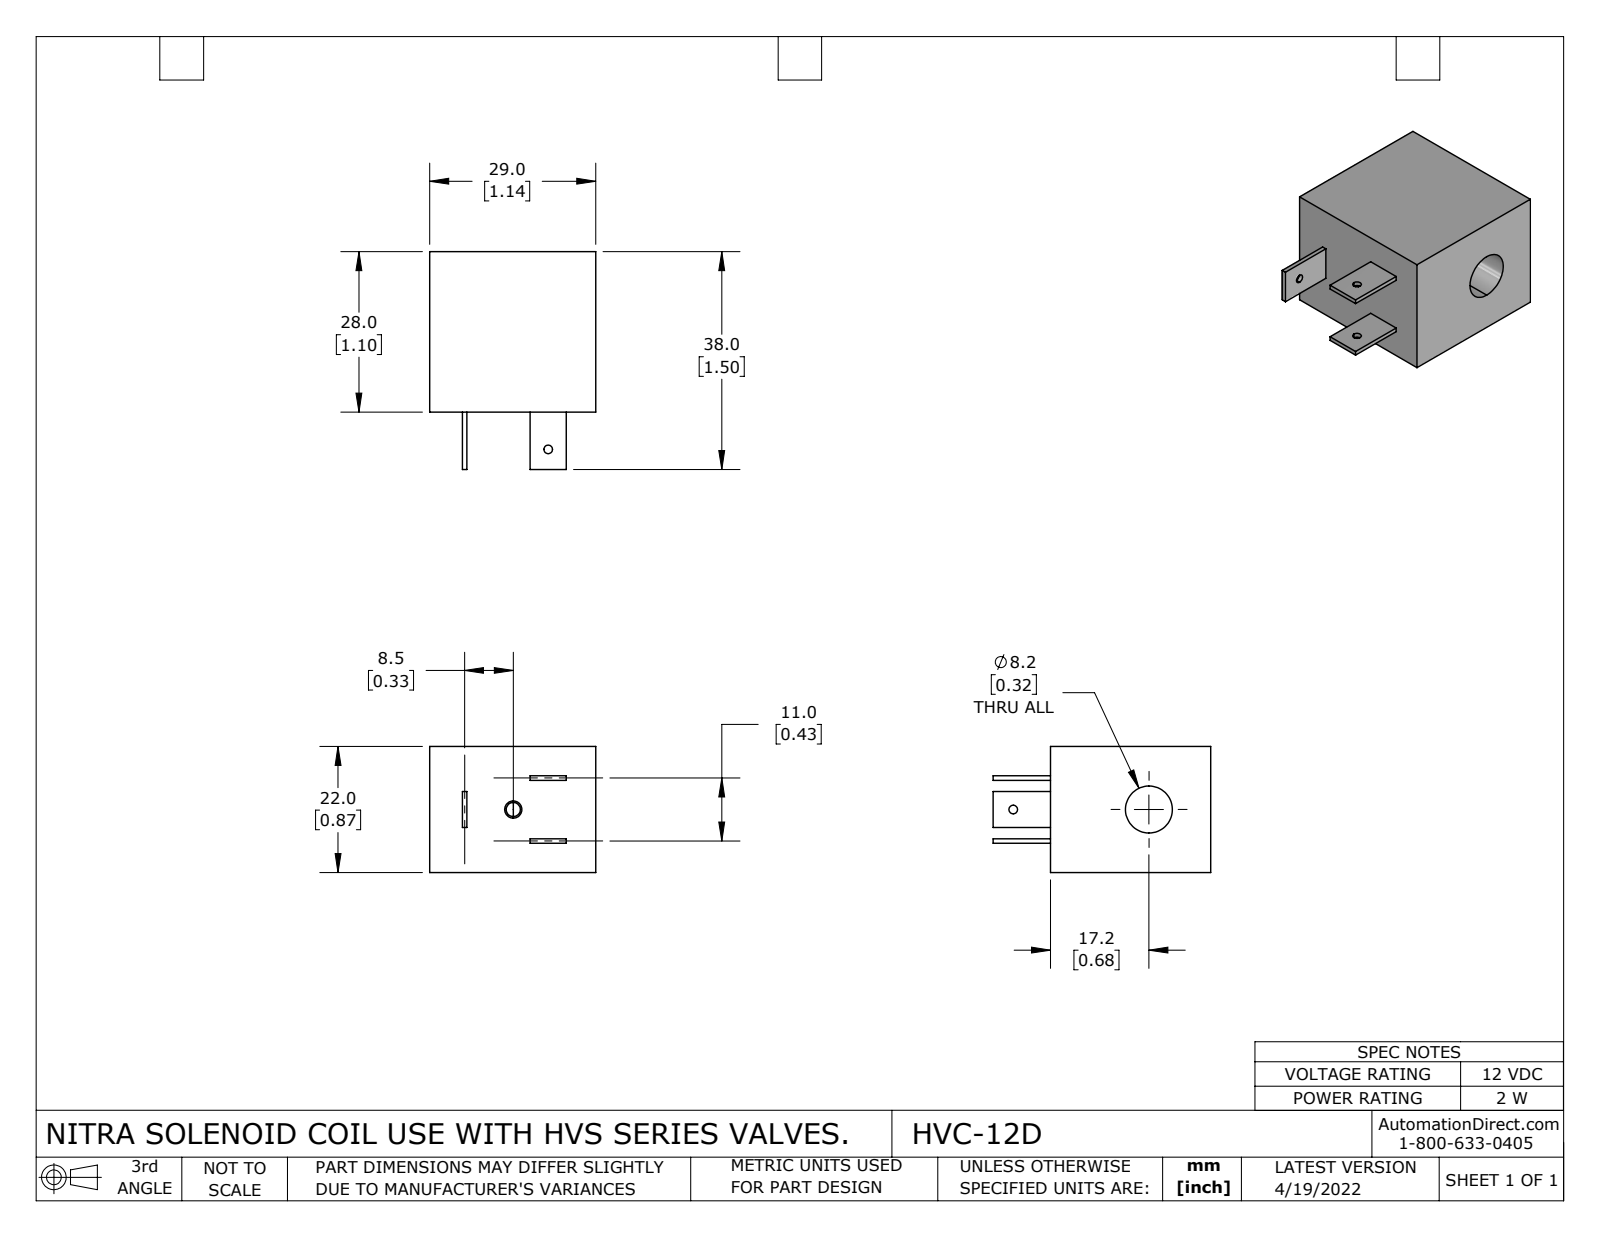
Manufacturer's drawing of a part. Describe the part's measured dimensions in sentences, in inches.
The part is named "HVC-12D". Its 3-D file was written by "SolidWorks 2021 (CONFIG_CONTROL_DESIGN)". It is 1 solid with 35 faces: 21 planar, 10 cylindrical and 4 other. Overall it measures 1.496 by 1.142 by 0.866 inches. Its volume is 1.004 cubic inches and its surface area 8.119 square inches. Round holes: 2 of diameter 0.059, 1 of diameter 0.097, 1 of diameter 0.323. The main face-to-face distances are 0.866, 1.102, 1.142, 0.031, 0.201, 0.232, 0.634, 0.665, 0.433, 0.224. The hole center spacings are 0.933.
